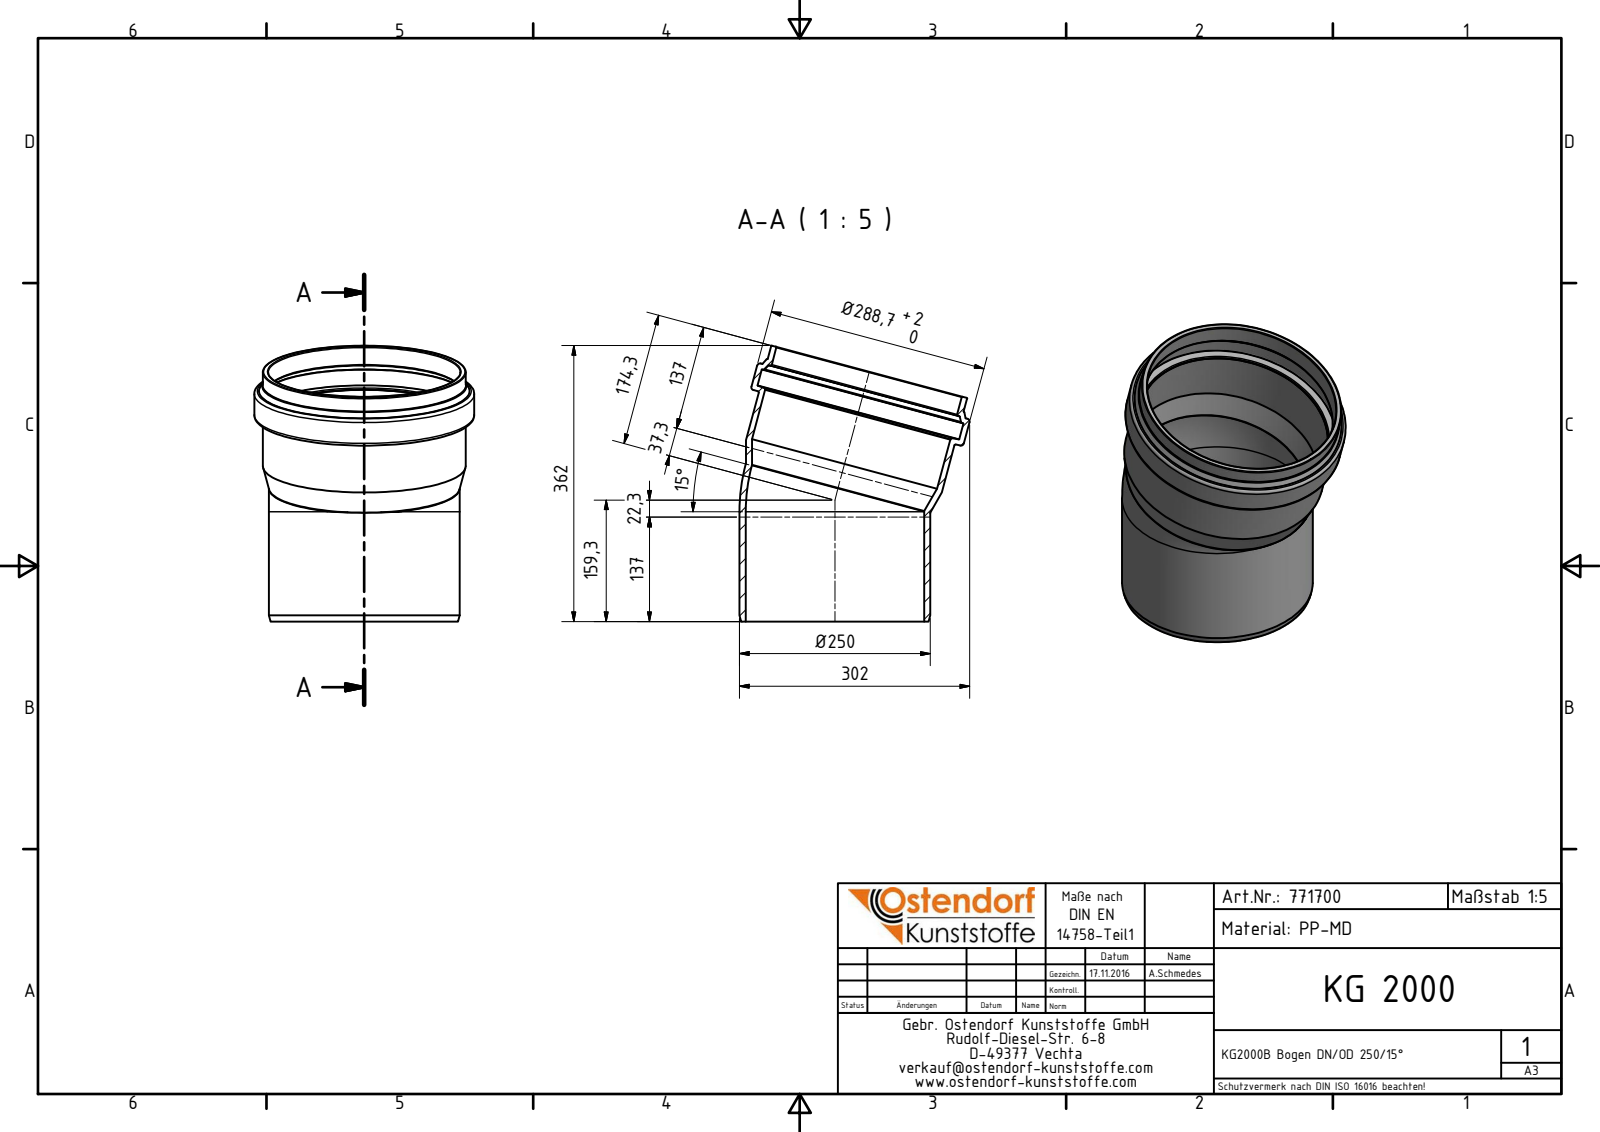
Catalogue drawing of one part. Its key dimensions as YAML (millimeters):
part_name: "771700 KG2000B Bogen DN_OD 250_15°"
step_written_by: "Autodesk Inventor 2016 (AUTOMOTIVE_DESIGN)"
units: millimeters
bodies: {solids: 1, faces: 41, planar: 5, cylindrical: 11, other: 25}
overall_size: [362, 302, 288.7]
volume: 2108000
surface_area: 565218
round_holes:
  - {diameter: 234.3, count: 2}
  - {diameter: 252.1, count: 2}
  - {diameter: 251.7, count: 1}
  - {diameter: 274.3, count: 1}
round_bosses_or_shafts:
  - {diameter: 250.3, count: 2}
  - {diameter: 288.7, count: 1}
  - {diameter: 266.5, count: 1}
  - {diameter: 266.1, count: 1}
face_to_face_distances: [62.61, 36.31, 26.3, 4.21, 32.1, 58.4]
